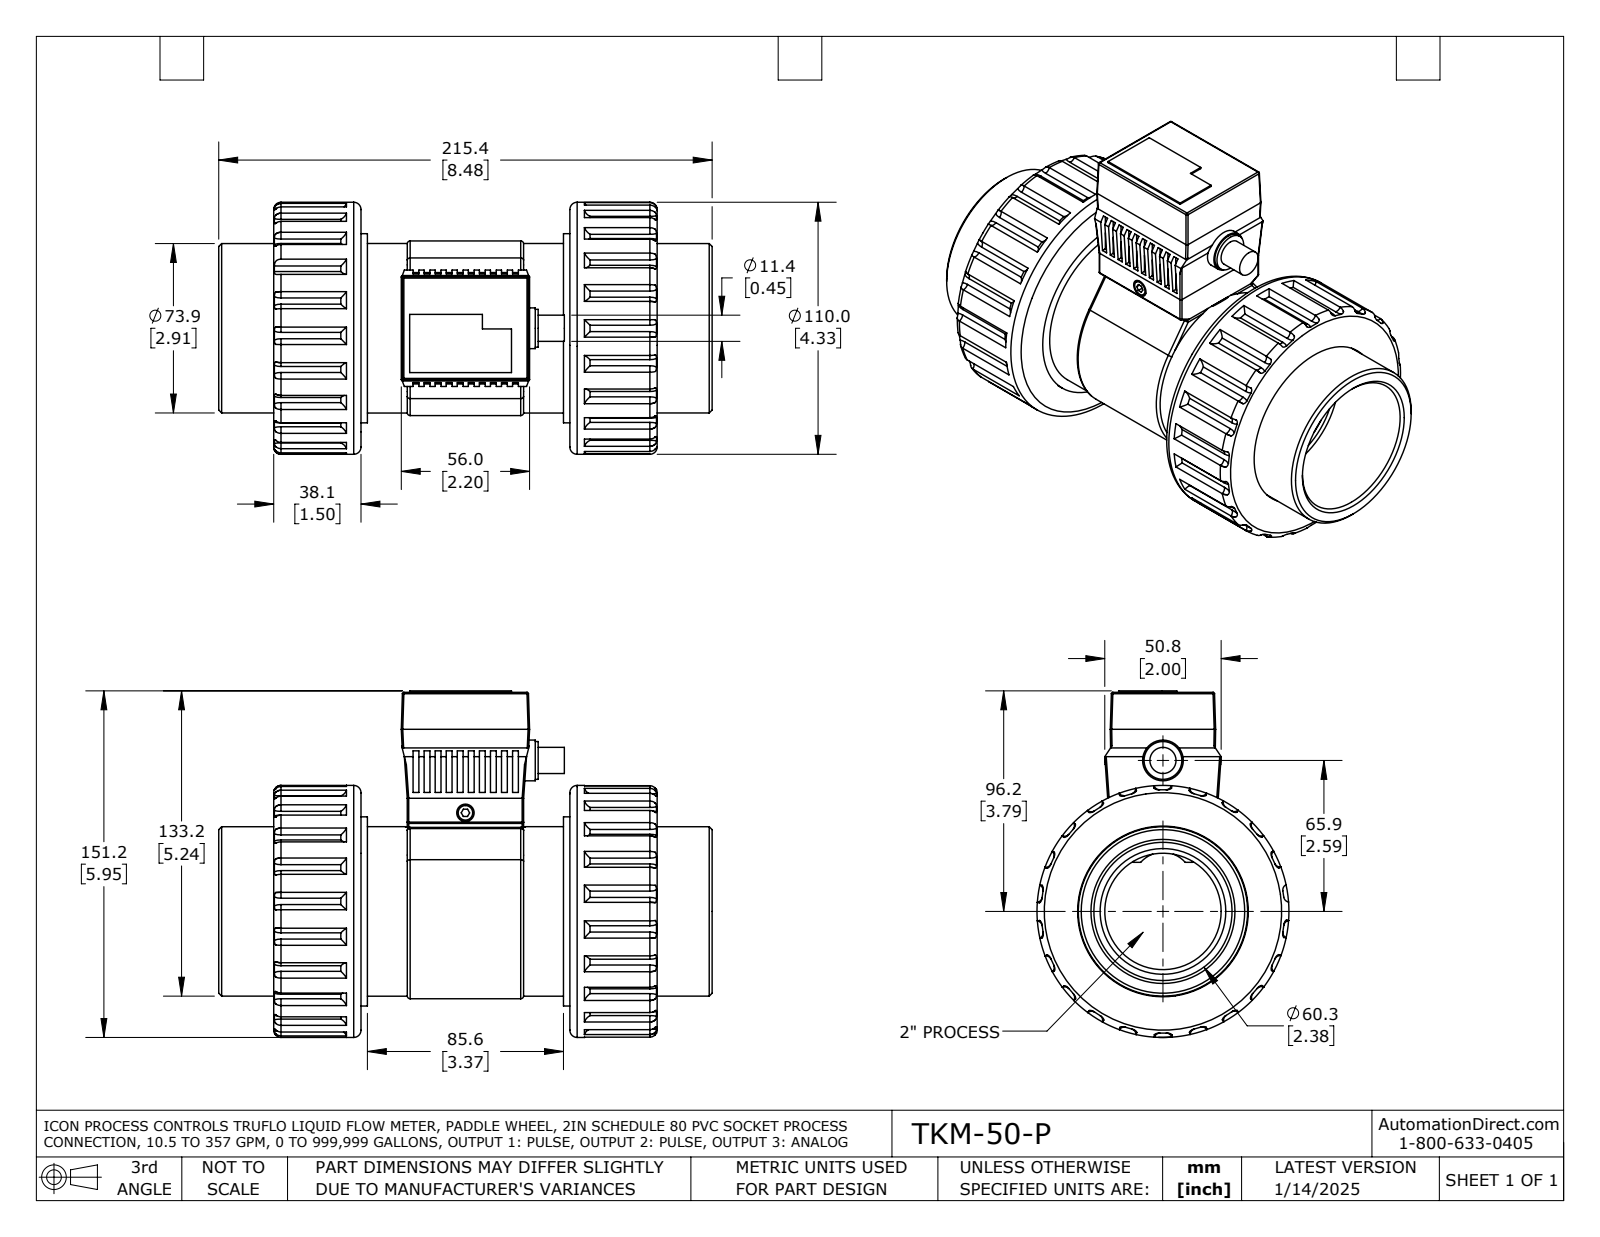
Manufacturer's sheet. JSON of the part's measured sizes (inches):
{"part_name": "TKM-50-P", "step_written_by": "SolidWorks 2021 (AUTOMOTIVE_DESIGN)", "units": "inches", "bodies": {"solids": 9, "faces": 751, "planar": 240, "cylindrical": 223, "other": 288}, "overall_size": [8.48, 5.954, 4.33], "volume_in3": 61.14, "surface_area_in2": 312.1, "round_holes": [[0.128, 4], [0.3, 1], [1.1, 1], [1.2, 1], [2, 1], [2.16, 1], [2.375, 1], [2.88, 1], [2.933, 1], [2.979, 1]], "round_bosses_or_shafts": [[4.33, 1], [3.25, 1], [3.08, 1], [2.913, 1], [2.91, 1], [2.55, 1], [1.024, 1], [0.7, 1]], "partial_cylinders_radius": [[0.1, 88], [0.025, 26], [0.05, 8], [0.465, 1], [0.512, 1], [1.5, 1]], "face_to_face_distances": [0.71, 5.88, 1.5, 5.09, 0.79, 4.38, 5.17, 6.59, 3.59, 0.1], "hole_center_spacings": [0.979, 1.181, 1.561, 1.957]}
